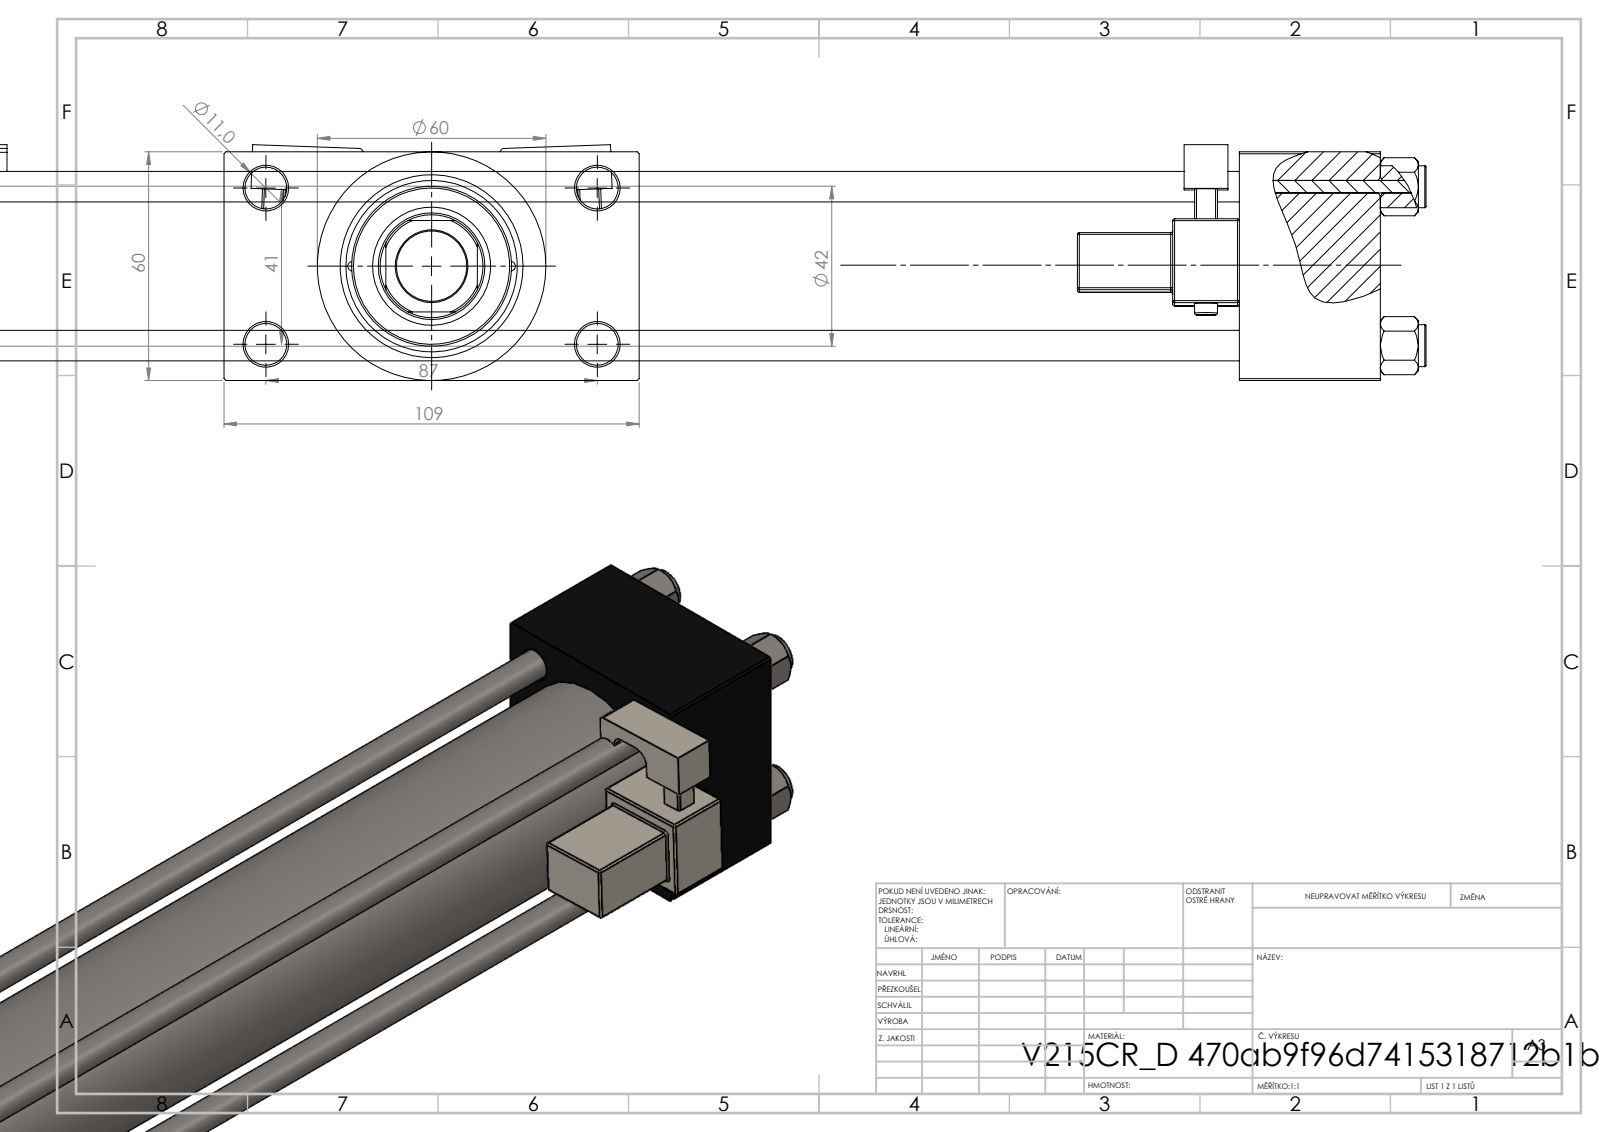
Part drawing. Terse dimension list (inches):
name: V215CR_D_TYCINKA; V215_VC_A; NUT_M5_D; V215CR_VCP_D (+2 more)
written by: SolidWorks 2019 (CONFIG_CONTROL_DESIGN)
unit: in
bodies: 13 solids, 1268 faces (560 planar, 152 cylindrical, 556 other)
size: 18.307 × 4.291 × 2.437
volume: 55.63 in³; area: 417.9 in²
holes: 4× ⌀0.315, 4× ⌀0.433, 2× ⌀0.098, 2× ⌀0.276, 2× ⌀0.656, 2× ⌀0.945, 1× ⌀0.728, 1× ⌀1.102, 1× ⌀1.22, 1× ⌀1.575, 1× ⌀1.772
bosses: 4× ⌀0.433, 2× ⌀0.236, 1× ⌀2.362, 1× ⌀1.811, 1× ⌀1.654
rounds: 48× R0.02, 2× R0.039, 2× R0.098, 2× R0.157, 1× R0.531
face distances: 2.362, 13.307, 0.965, 3.327, 1.457, 14.764, 16.457, 15, 1.693, 4.291
hole spacings: 0.821, 0.892, 1.161, 1.206, 1.642, 1.832, 1.856, 1.893
